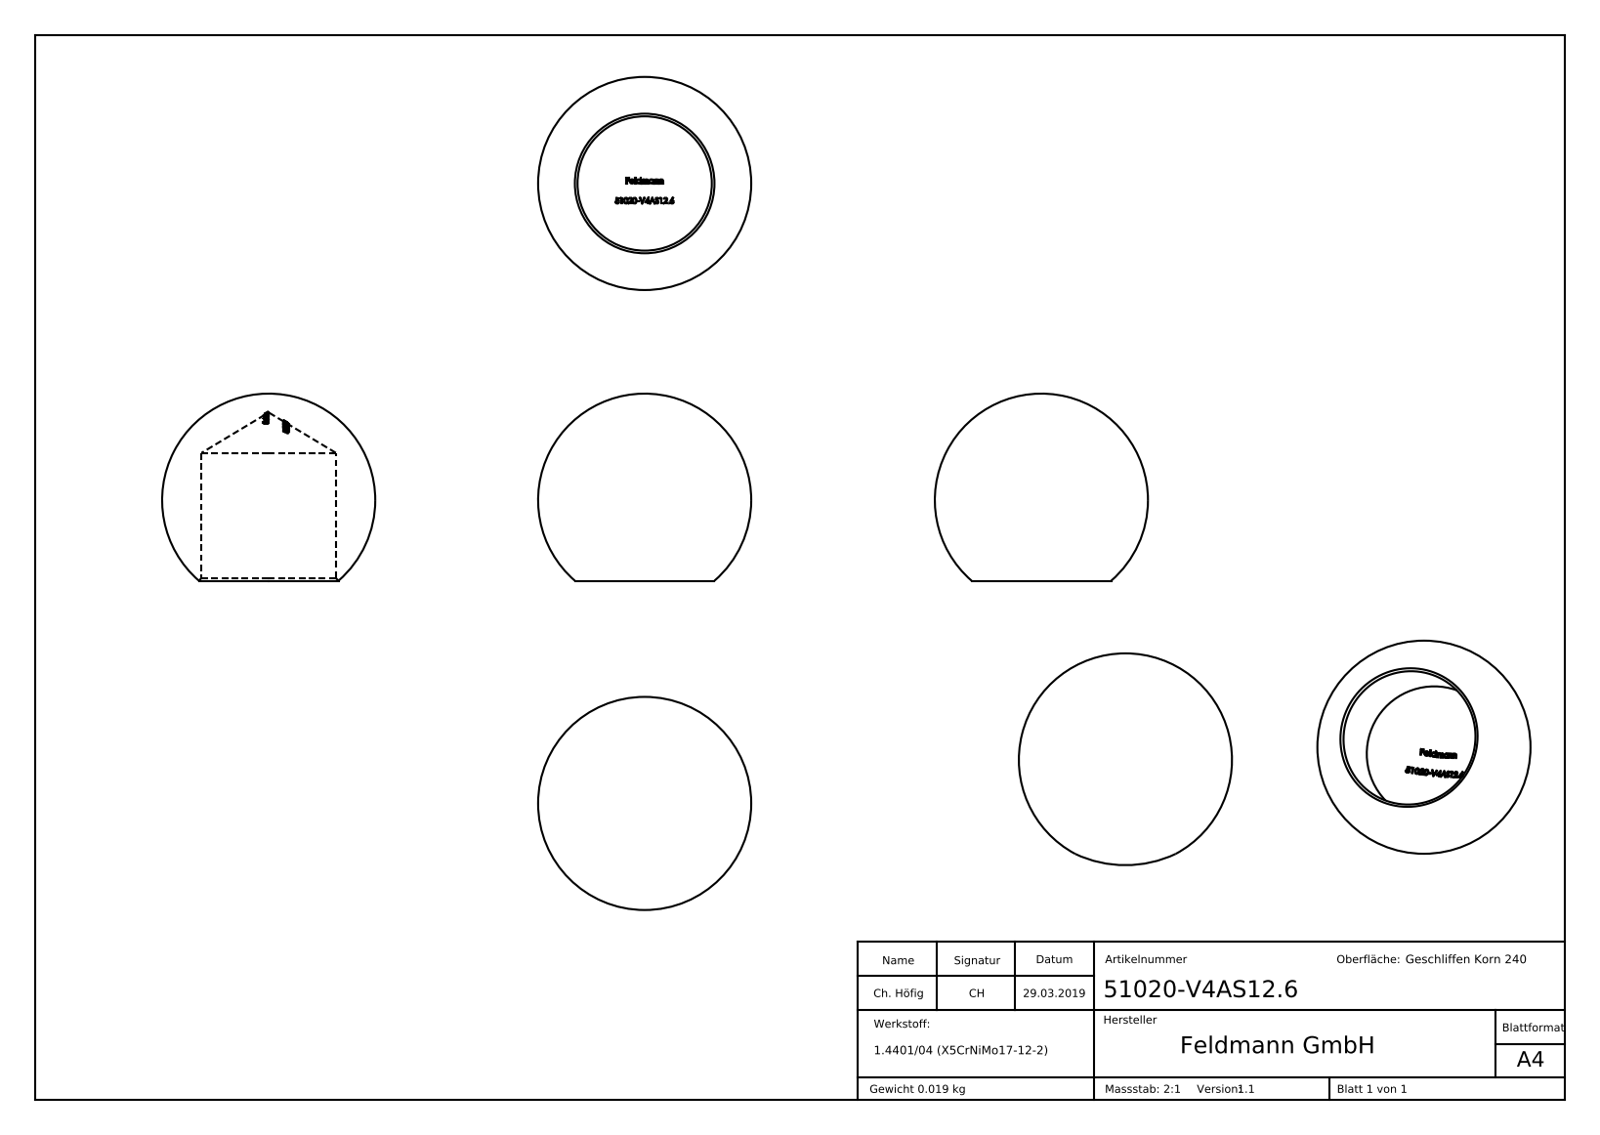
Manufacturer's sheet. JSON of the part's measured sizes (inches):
{"part_name": "51020-V4AS12.6", "step_written_by": "SolidWorks 2015 (CONFIG_CONTROL_DESIGN)", "units": "inches", "bodies": {"solids": 1, "faces": 283, "planar": 124, "cylindrical": 2, "other": 157}, "overall_size": [0.787, 0.787, 0.691], "volume_in3": 0.144, "surface_area_in2": 2.686, "round_holes": [[0.496, 1]], "face_to_face_distances": [0.076, 0.072, 0.074, 0.05, 0.098, 0.021, 0.022, 0.053, 0.047, 0.026]}
